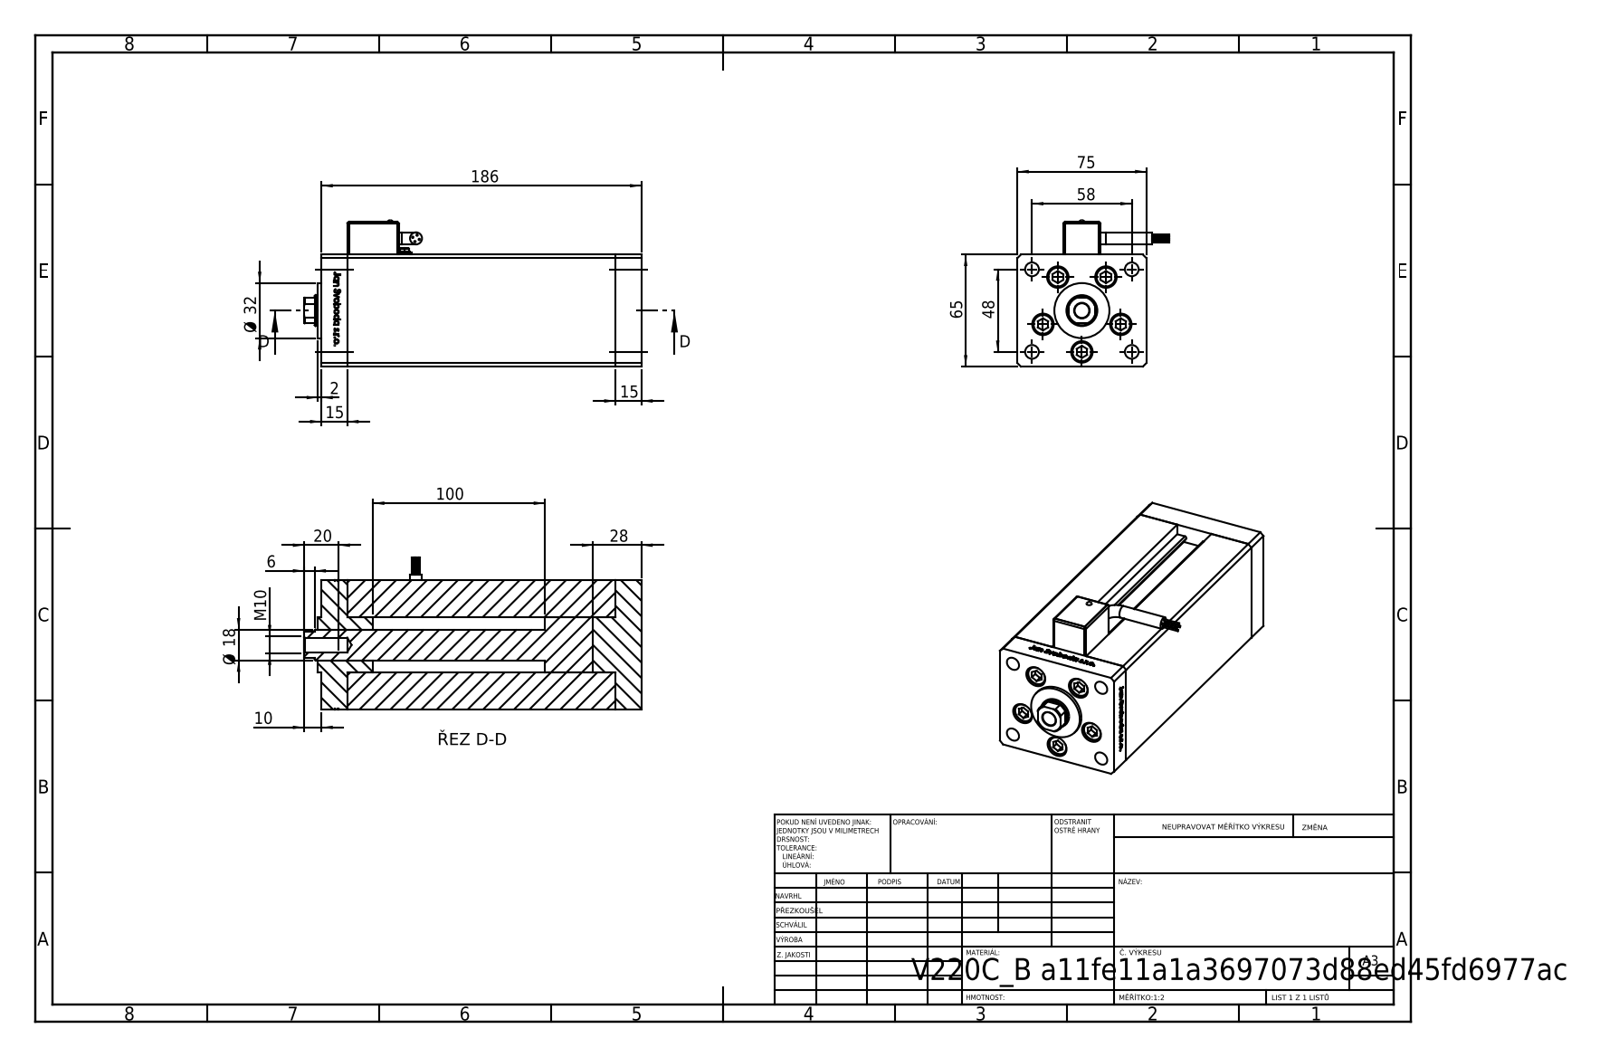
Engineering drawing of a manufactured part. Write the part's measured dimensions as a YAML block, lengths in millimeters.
part_name: "V220C_B MIDDLE; V220C_VC_B; ALLEN BOLT; V220C BACK_B (+2 more)"
step_written_by: "SolidWorks 2019 (CONFIG_CONTROL_DESIGN)"
units: millimeters
bodies: {solids: 15, faces: 1285, planar: 501, cylindrical: 192, other: 592}
overall_size: [196, 88.3, 85.1]
volume: 823817
surface_area: 142161
round_holes:
  - {diameter: 9, count: 5}
  - {diameter: 12.5, count: 5}
  - {diameter: 8, count: 4}
  - {diameter: 2, count: 2}
  - {diameter: 13.16, count: 2}
  - {diameter: 3.6, count: 1}
  - {diameter: 5, count: 1}
  - {diameter: 7, count: 1}
  - {diameter: 8.5, count: 1}
  - {diameter: 18, count: 1}
round_bosses_or_shafts:
  - {diameter: 8, count: 5}
  - {diameter: 0.85, count: 4}
  - {diameter: 7, count: 2}
  - {diameter: 32, count: 1}
  - {diameter: 6, count: 1}
  - {diameter: 3.5, count: 1}
  - {diameter: 2.5, count: 1}
partial_cylinders:
  - {radius: 1, count: 14}
  - {radius: 0.93, count: 2}
  - {radius: 4, count: 2}
  - {radius: 8.5, count: 1}
face_to_face_distances: [75, 65, 15, 156, 171, 186, 4, 54.5, 10.5, 58.5]
hole_center_spacings: [24, 37.64, 15.67, 17.22, 27.71, 28.83, 29, 32.63]
